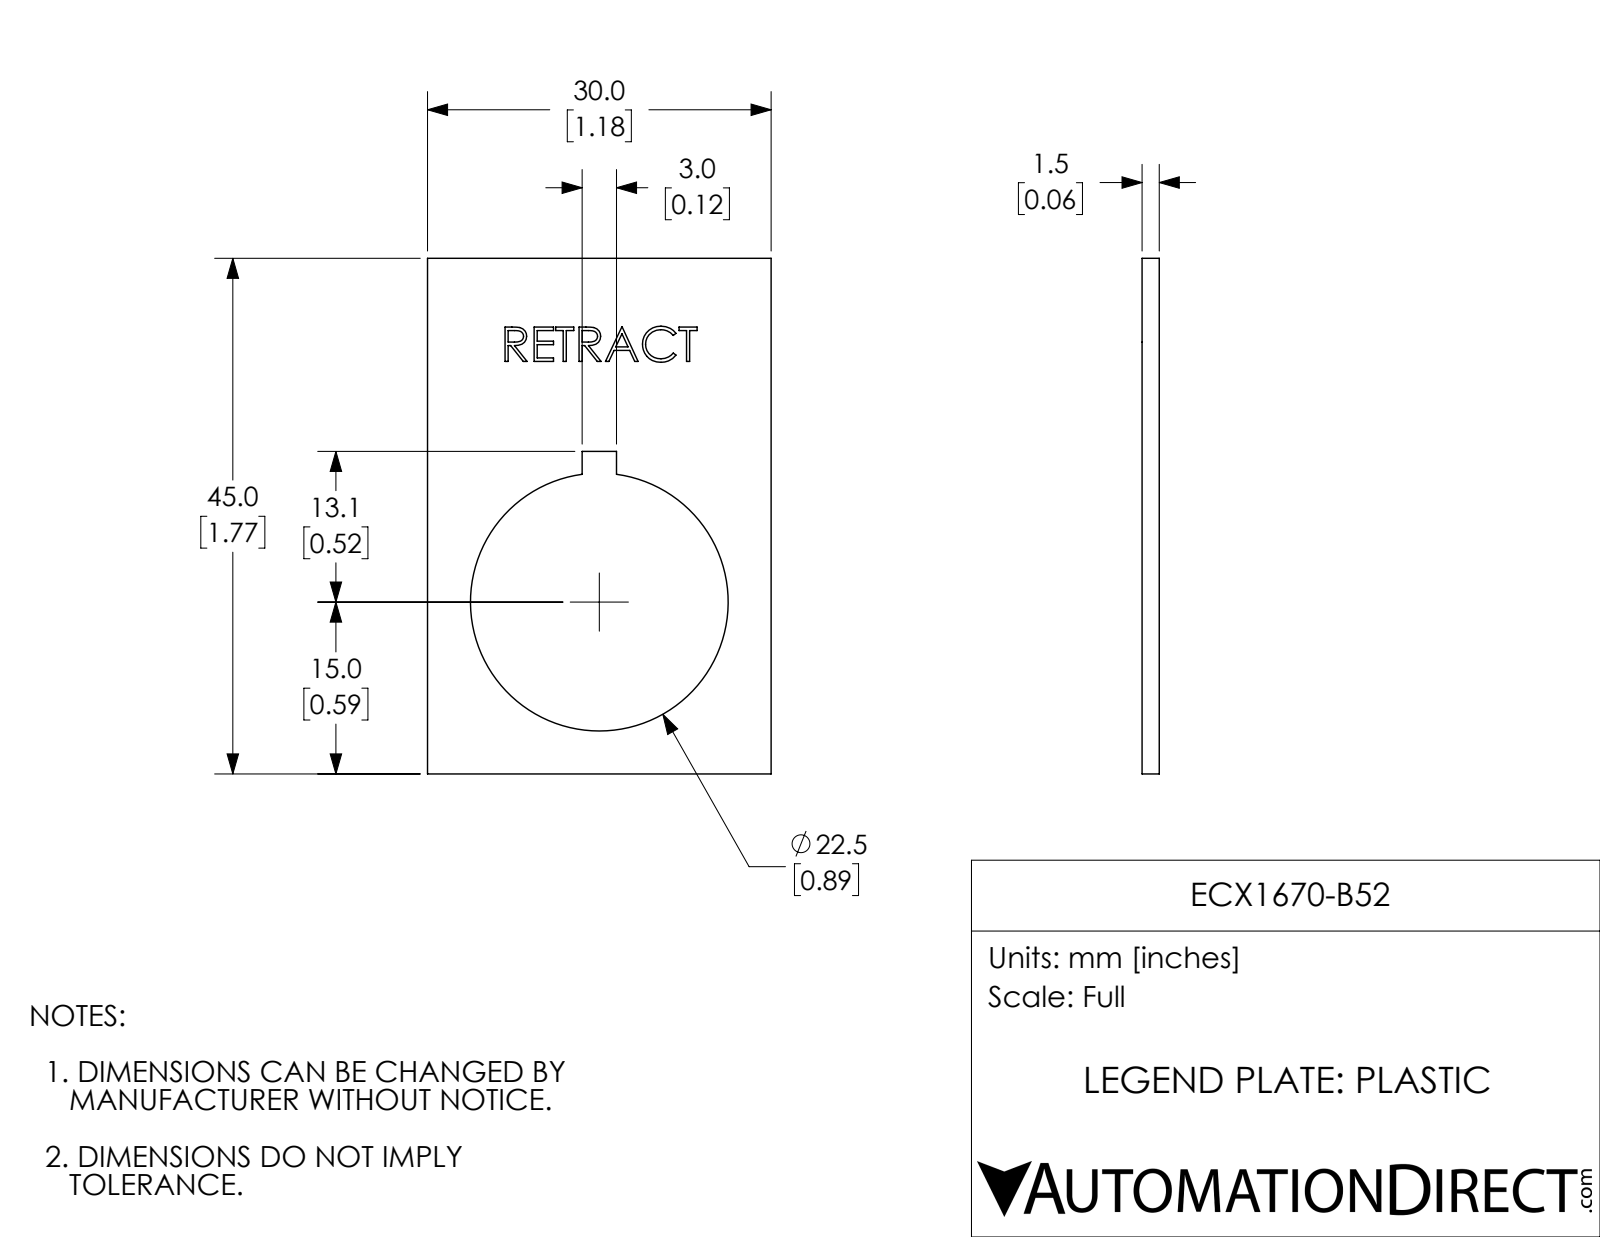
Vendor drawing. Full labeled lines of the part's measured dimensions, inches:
Part name (STEP PRODUCT): ECX1670-B52
STEP written by: SolidWorks 2017 (AUTOMOTIVE_DESIGN)
Units: inches
Bodies: 1 solid, 104 faces (82 planar, 3 cylindrical, 19 other)
Overall size (bounding box): 1.772 × 1.181 × 0.059
Volume: 0.087 in³ · Surface area: 3.461 in²
Round holes (diameter × count): ⌀0.886 ×1
Main face-to-face distances: 0.059, 1.181, 1.772, 0.058, 0.65, 0.531, 1.108, 0.663, 0.118, 0.1
